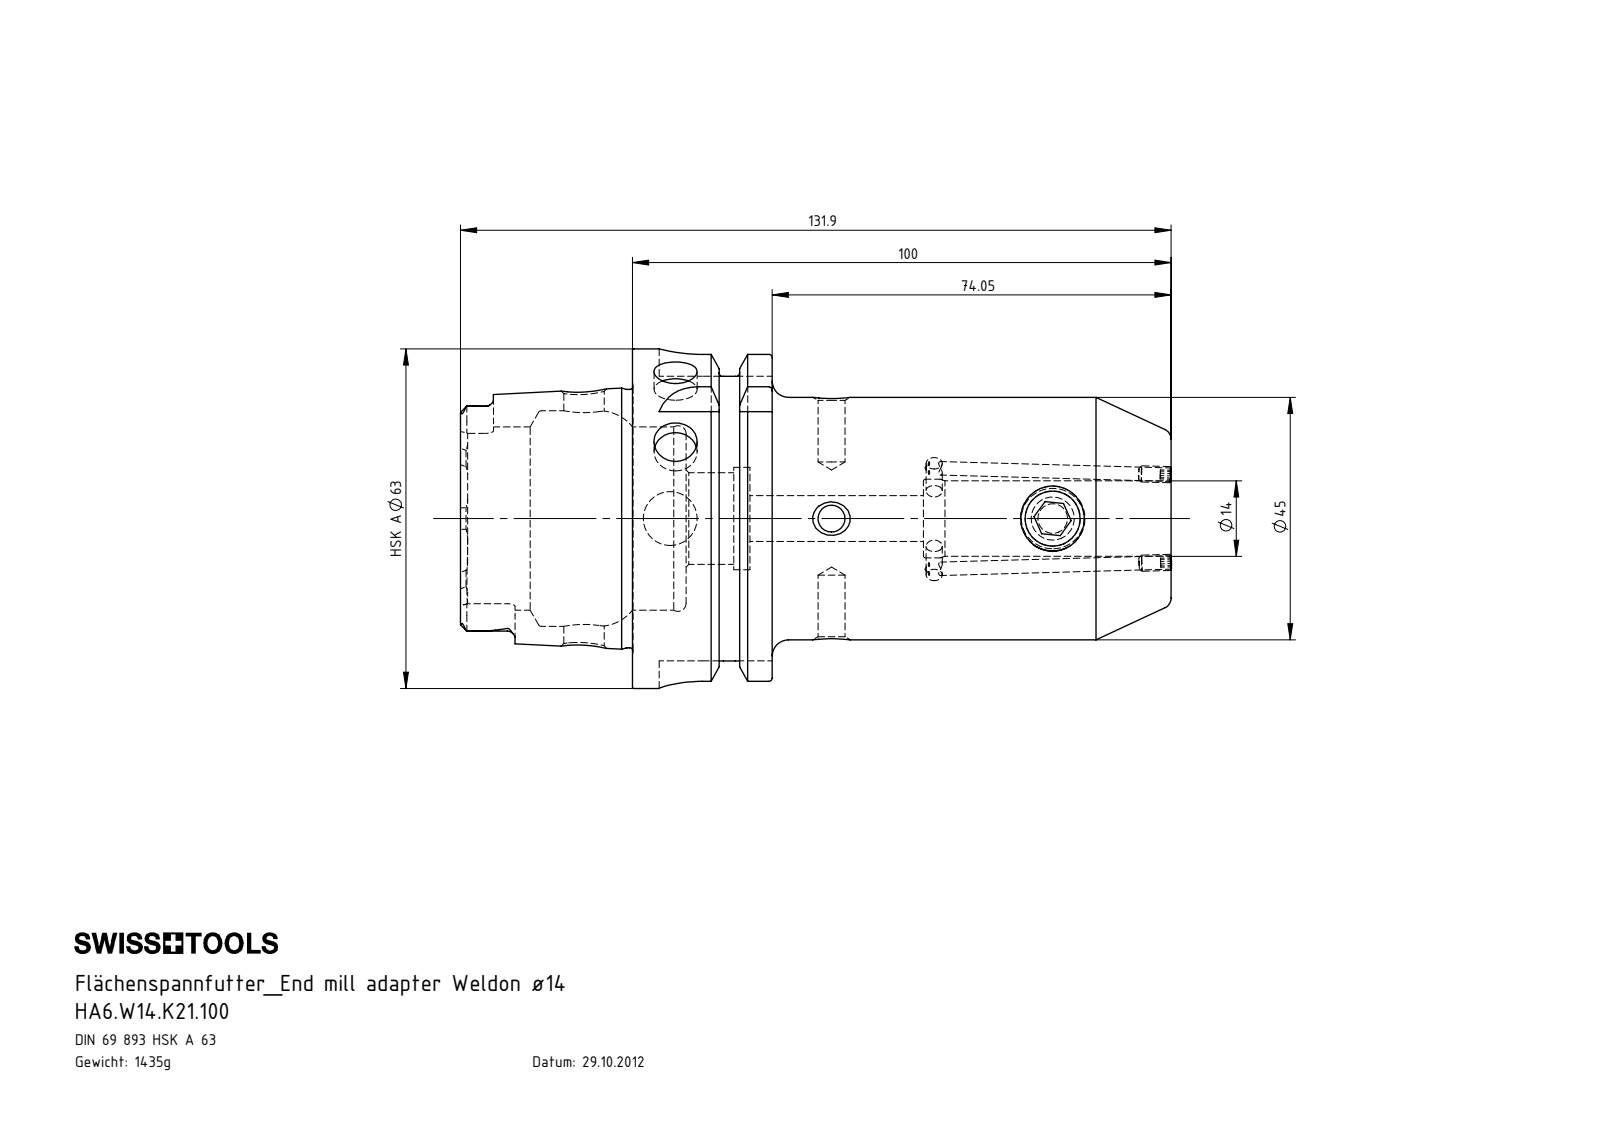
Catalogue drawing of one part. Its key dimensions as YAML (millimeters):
part_name: "HA6-W14.K21.100; ERU-CJ2.001.006; W12-ER1.001.016; HA6-W14.K21.100_A_Fertigbearbeitung"
step_written_by: "SolidWorks 2012 (CONFIG_CONTROL_DESIGN)"
units: millimeters
bodies: {solids: 4, faces: 286, planar: 77, cylindrical: 81, other: 128}
overall_size: [131.98, 63, 63]
volume: 182829
surface_area: 37579
round_holes:
  - {diameter: 2.5, count: 2}
  - {diameter: 5, count: 2}
  - {diameter: 8, count: 2}
  - {diameter: 3, count: 1}
  - {diameter: 7.5, count: 1}
  - {diameter: 8.5, count: 1}
  - {diameter: 10, count: 1}
  - {diameter: 10.25, count: 1}
  - {diameter: 14, count: 1}
  - {diameter: 14.6, count: 1}
  - {diameter: 17, count: 1}
  - {diameter: 19, count: 1}
round_bosses_or_shafts:
  - {diameter: 3, count: 2}
  - {diameter: 63, count: 1}
  - {diameter: 54.95, count: 1}
  - {diameter: 47.94, count: 1}
  - {diameter: 45, count: 1}
  - {diameter: 12, count: 1}
partial_cylinders:
  - {radius: 1.4, count: 6}
  - {radius: 2.88, count: 4}
  - {radius: 8, count: 4}
face_to_face_distances: [25.95, 16, 9.95, 100, 90.05, 74.05, 31.9, 41.85, 57.85, 131.9]
hole_center_spacings: [29.95, 41.05, 45.95, 71]
